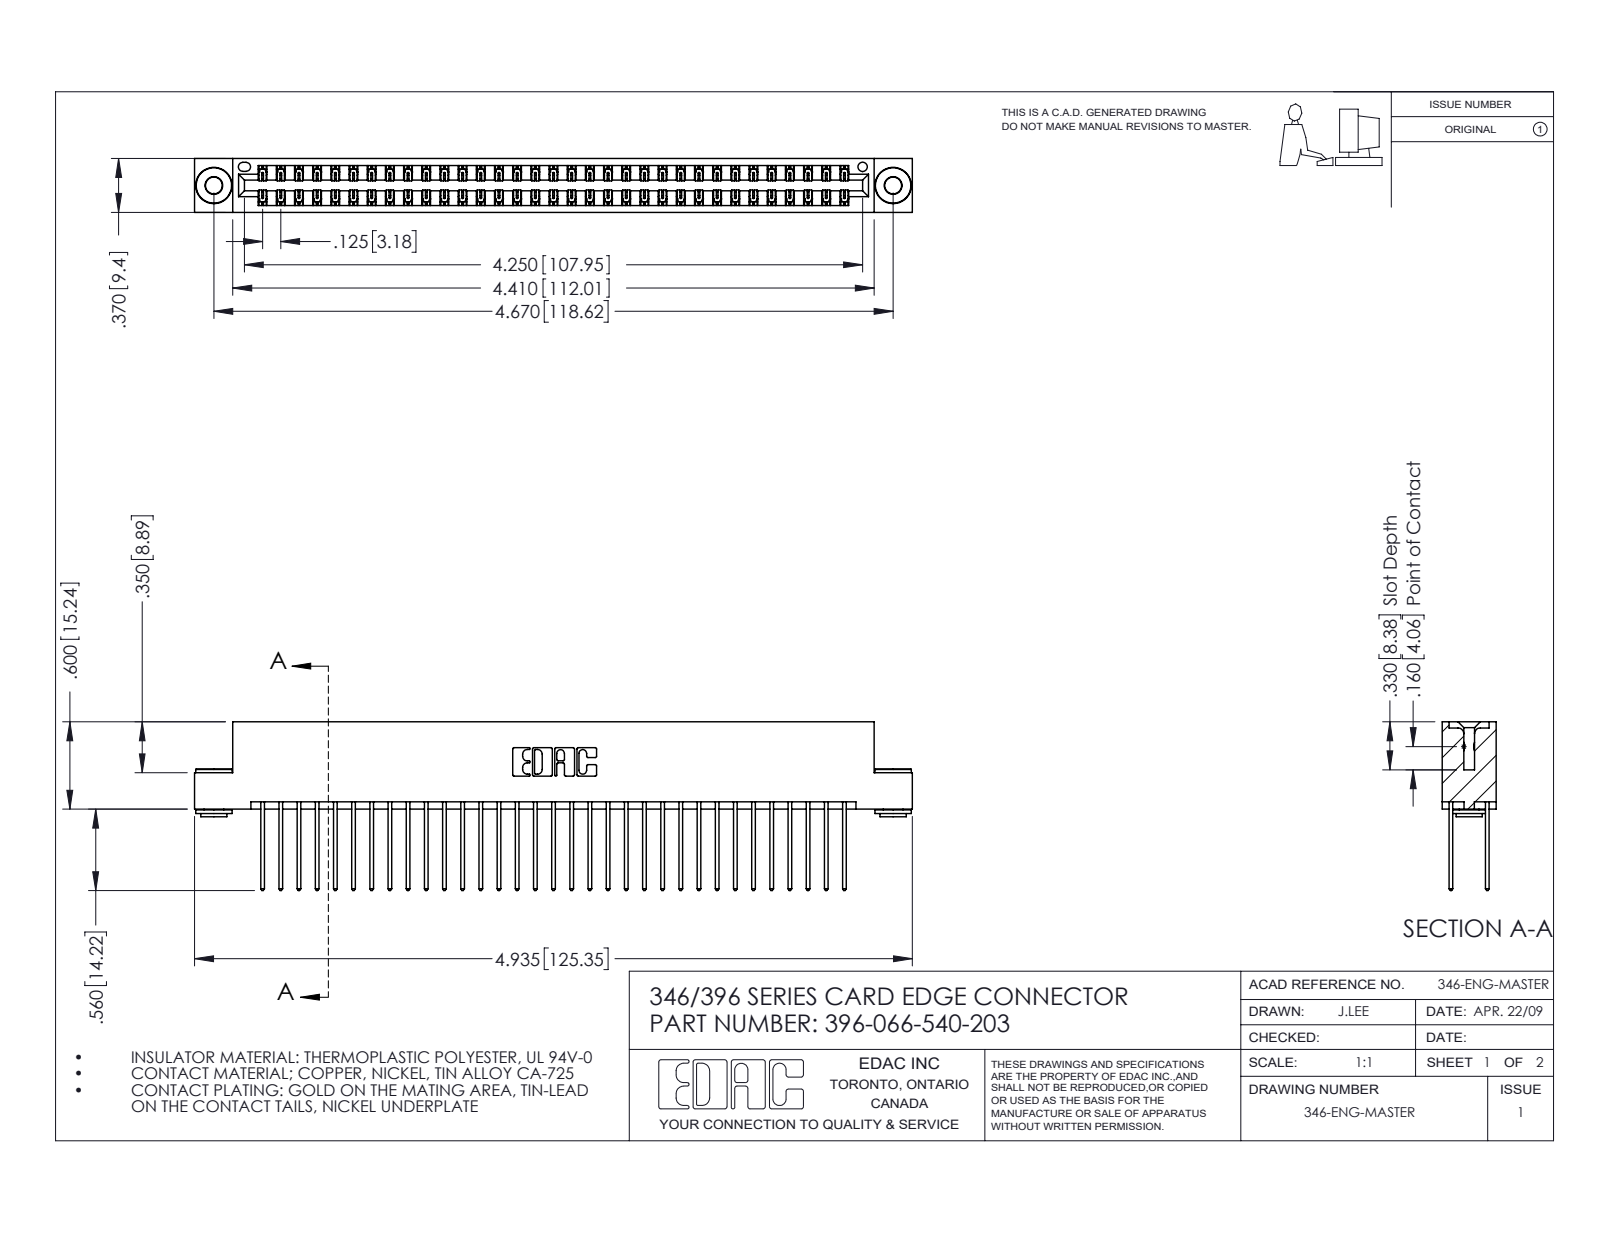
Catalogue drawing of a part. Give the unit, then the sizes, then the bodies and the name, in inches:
Units: inches
Overall size (bounding box): 4.935 × 1.16 × 0.37
Round holes (diameter × count): ⌀0.116 ×2, ⌀0.156 ×2, ⌀0.064 ×1
Round bosses / shafts (diameter × count): ⌀0.25 ×2, ⌀0.18 ×2, ⌀0.136 ×2
Partial cylindrical surfaces — rounded edges, fillets, slot ends (radius × count): R0.006 ×99, R0.01 ×66, R0.01 ×22, R0.007 ×6, R0.031 ×6, R0.026 ×3, R0.014 ×2, R0.022 ×2
Main face-to-face distances: 0.048, 0.322, 0.25, 0.025, 0.072, 0.298, 0.37, 0.275, 0.148, 0.222
Hole centre spacings: 0.246, 4.462, 4.67
Volume: 0.758 in³ · Surface area: 28.41 in²
Bodies: 69 solids, 3592 faces (2396 planar, 1188 cylindrical, 8 other)
Part name (STEP PRODUCT): 396-066-540-203; 345-250-002_345-250-002-102; 345-292-001_345-293-140; 346 Part_Flush Mounting Lugs - 0.156 Dia-TH
STEP written by: SolidWorks 2016 (CONFIG_CONTROL_DESIGN)
